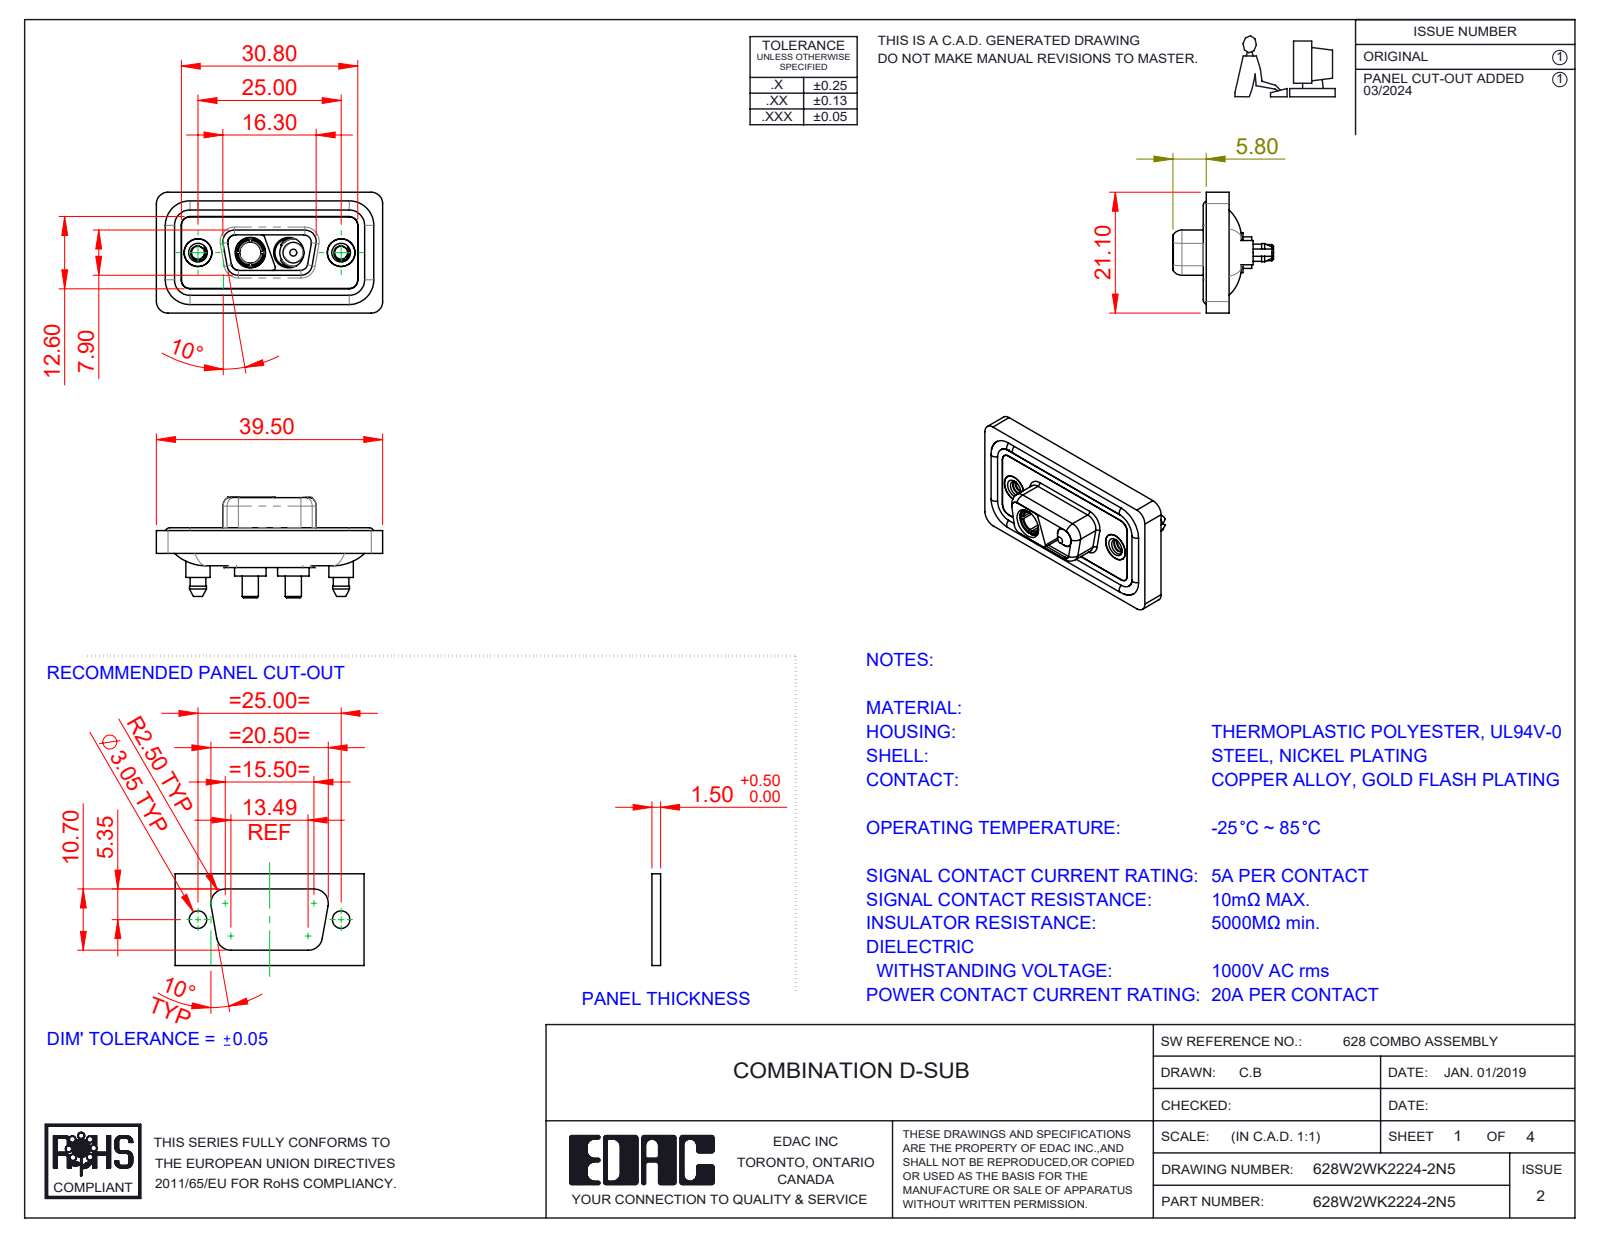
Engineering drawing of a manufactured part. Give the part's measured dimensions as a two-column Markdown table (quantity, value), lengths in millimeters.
| quantity | value |
| --- | --- |
| part name | 628Combo Threaded Boardlock_5; Power Pin_20A S; 628Combo Shell Front_09 Contacts; 628Combo Housing_2WK2 (+4 more) |
| STEP written by | SolidWorks 2023 (CONFIG_CONTROL_DESIGN) |
| units | millimeters |
| bodies | 11 solids, 550 faces (160 planar, 263 cylindrical, 127 other) |
| overall size | 39.5 × 21.1 × 17.55 |
| volume | 4 737 mm³ |
| surface area | 7 677 mm² |
| round holes (diameter × count) | 4.85 × 4, 2.26 × 2, 4 × 2, 4.05 × 2, 5 × 2, 5.3 × 2, 3.7 × 1 |
| round bosses / shafts (diameter × count) | 1.6 × 4, 5.5 × 2, 5.4 × 2, 5.2 × 2, 4.95 × 2, 4.8 × 2, 4.75 × 2, 4.25 × 2 |
| partial cylindrical surfaces (radius × count) | 1.5 × 24, 2 × 18, 1.6 × 10, 1.35 × 8, 0.5 × 6, 0.25 × 4, 0.6 × 4, 0.65 × 4 |
| main face-to-face distances | 0.4, 1.1, 2.9, 1.6, 0.5, 1.8, 5.65, 1.5, 4, 5.35 |
| hole center spacings | 9.14, 15.86, 6.72, 25 |
